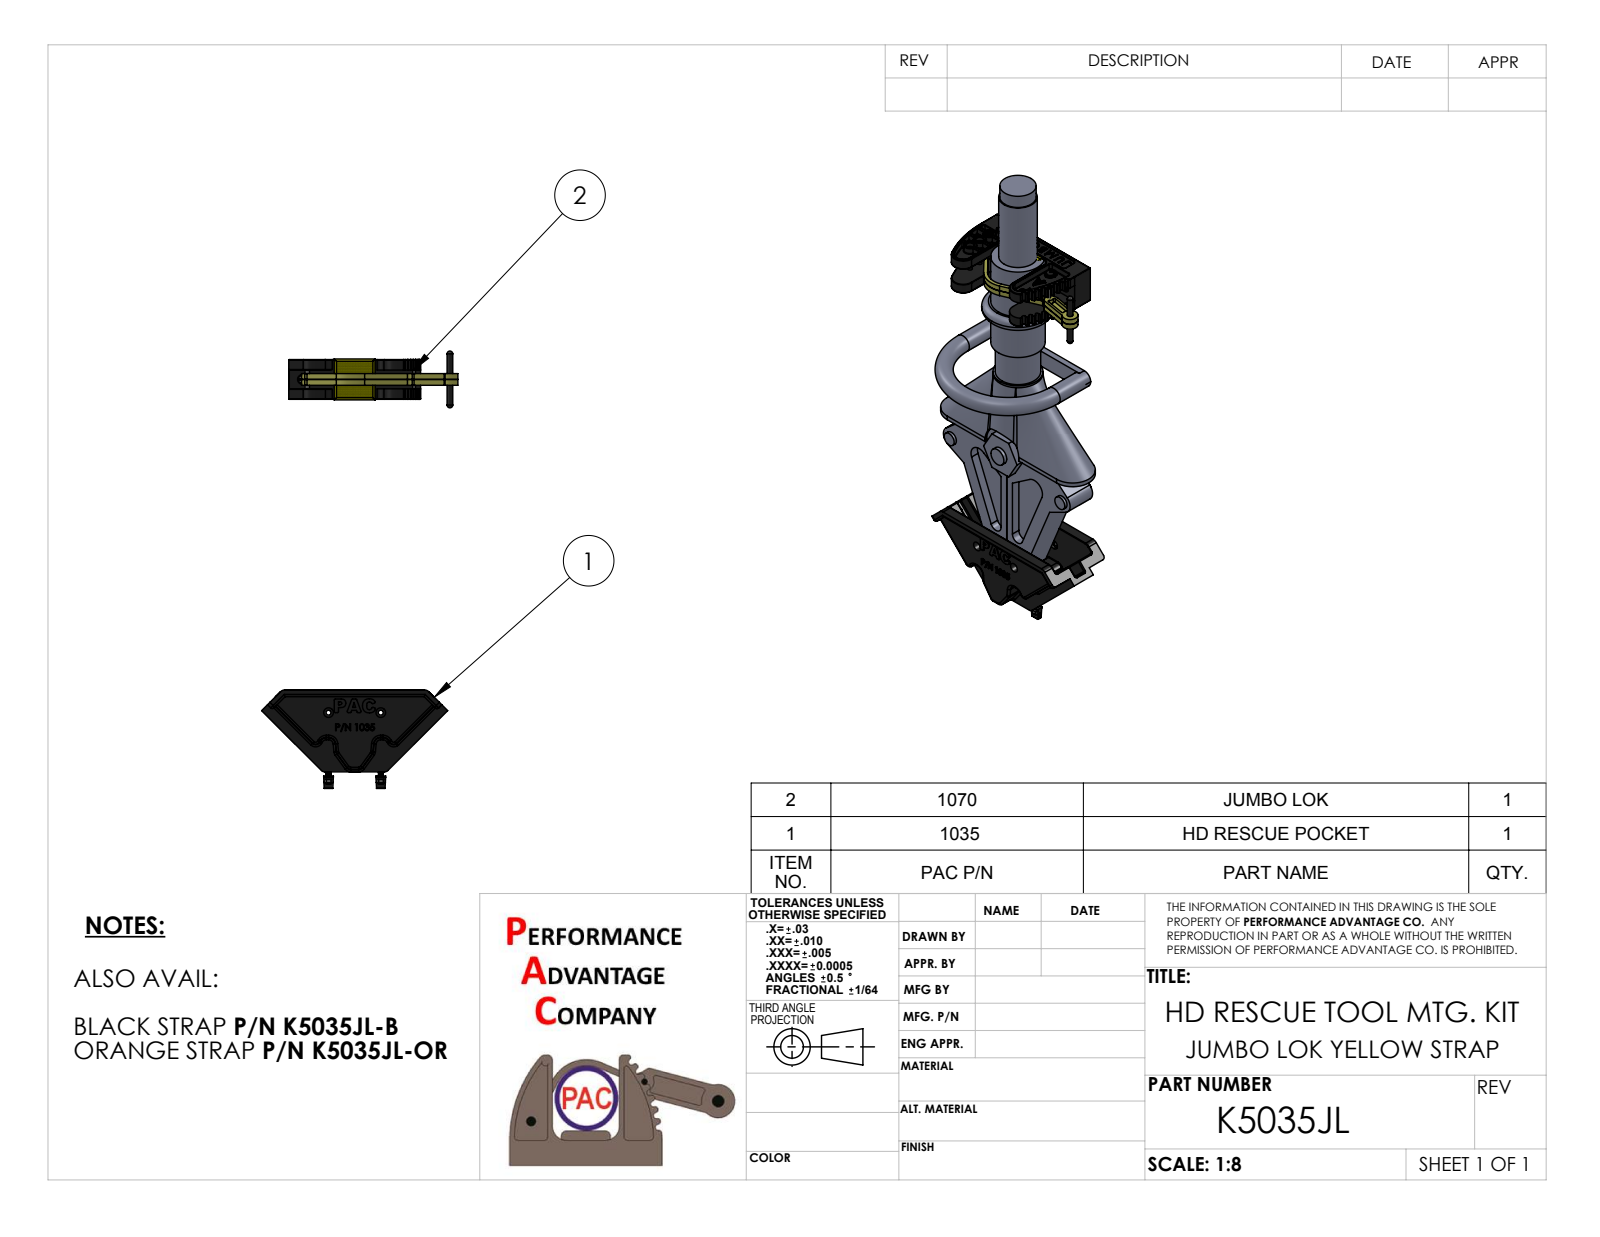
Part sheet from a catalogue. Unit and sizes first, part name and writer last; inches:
Units: inches
Overall size (bounding box): 38.611 × 12.88 × 12
Round holes (diameter × count): ⌀0.201 ×14, ⌀0.266 ×4, ⌀0.266 ×4, ⌀0.269 ×4, ⌀0.25 ×2, ⌀0.26 ×2, ⌀0.266 ×2, ⌀0.281 ×2, ⌀0.531 ×2, ⌀0.686 ×2, ⌀1 ×2, ⌀1.125 ×1
Round bosses / shafts (diameter × count): ⌀0.375 ×10, ⌀0.187 ×10, ⌀0.46 ×8, ⌀0.25 ×8, ⌀0.404 ×4, ⌀1.125 ×2, ⌀1 ×2, ⌀5.375 ×1
Partial cylindrical surfaces — rounded edges, fillets, slot ends (radius × count): R0.031 ×150, R0.125 ×62, R0.062 ×55, R0.063 ×35, R0.078 ×29, R0.25 ×27, R0.016 ×16, R0.375 ×16
Main face-to-face distances: 0.875, 6.459, 0.75, 5.709, 1.625, 4.833, 7.334, 0.125, 6.584, 5.583
Hole centre spacings: 2.875, 5.574, 5.495, 0.937, 0.938, 1.485, 1.716, 1.875
Volume: 797.9 in³ · Surface area: 1 884 in²
Bodies: 65 solids, 5667 faces (1791 planar, 1222 cylindrical, 2654 other)
Part name (STEP PRODUCT): 3017_HFBOLT 0.25-20x1.25x0.75-C; 7016; 1020-204; K5020 (+8 more)
STEP written by: SolidWorks 2014 (CONFIG_CONTROL_DESIGN)
